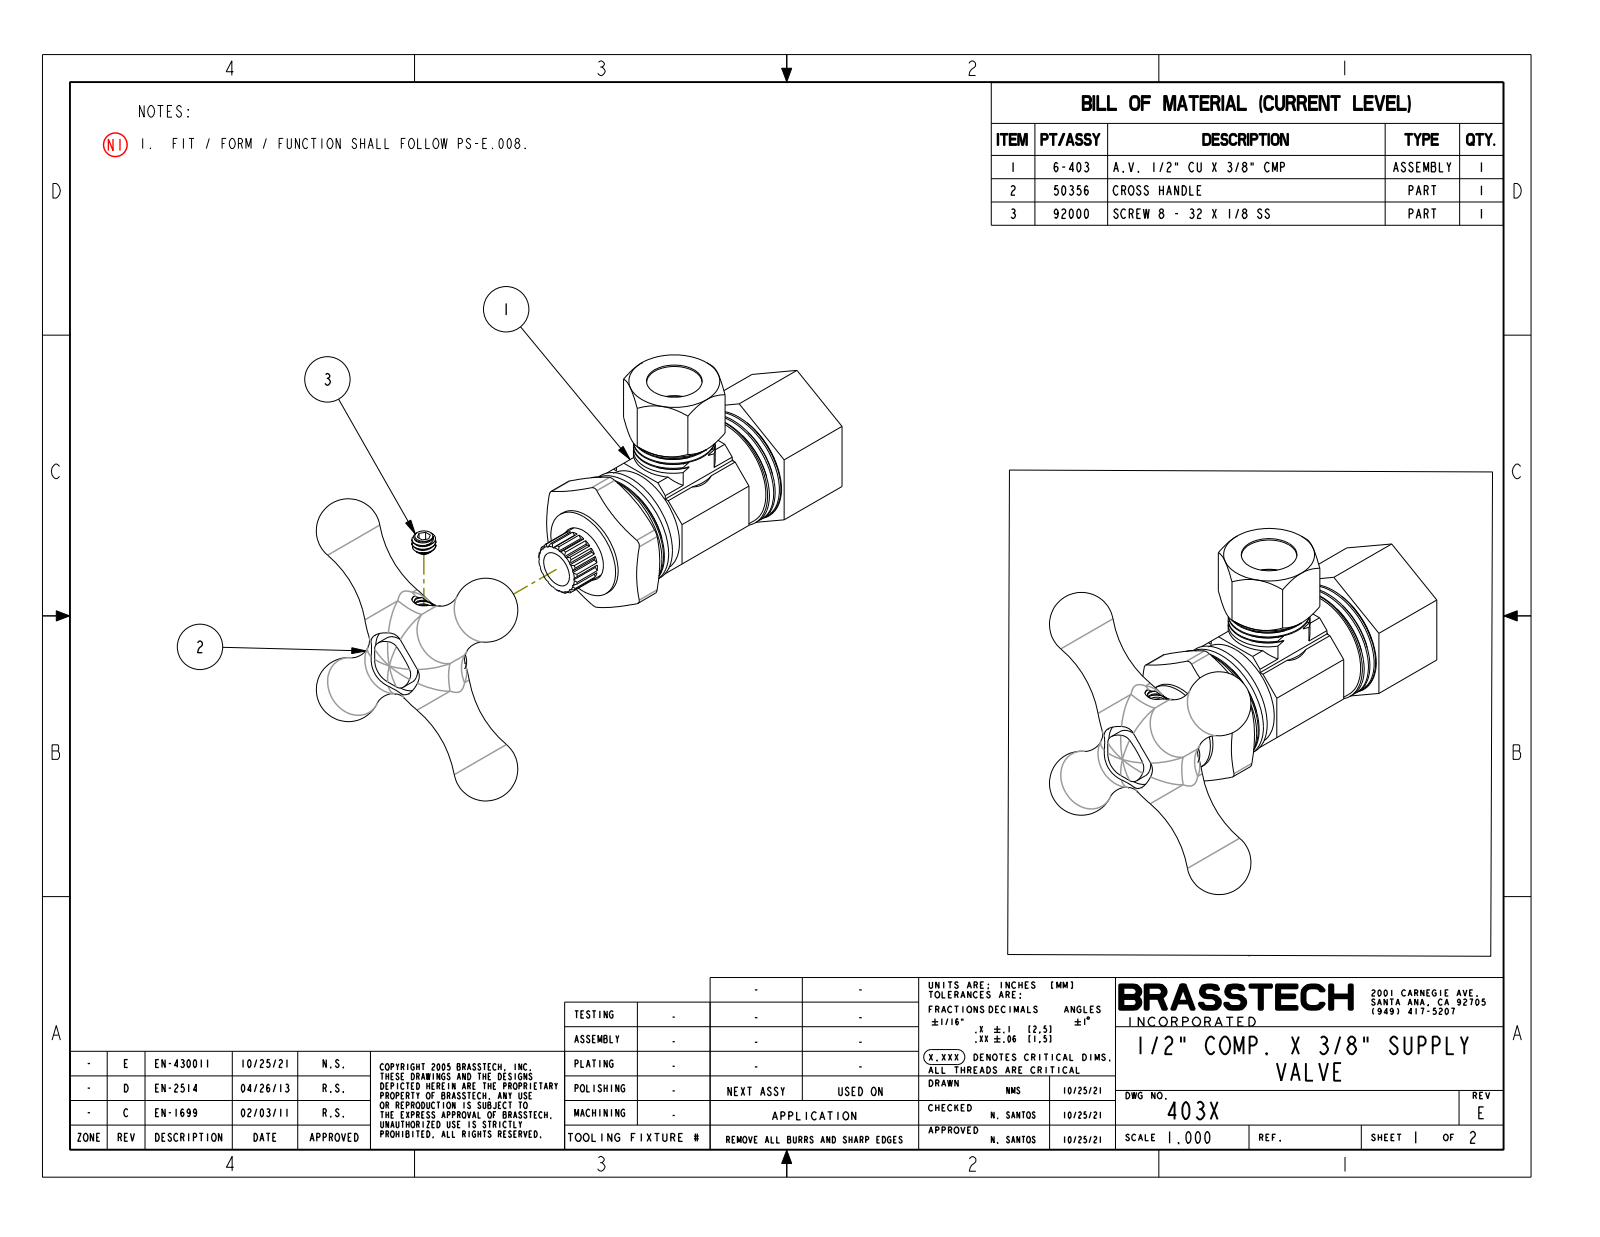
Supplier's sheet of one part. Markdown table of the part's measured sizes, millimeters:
| quantity | value |
| --- | --- |
| part name | 403X |
| STEP written by | CREO PARAMETRIC BY PTC INC, 2018500 (CONFIG_CONTROL_DESIGN) |
| units | millimeters |
| bodies | 3 solids, 772 faces (255 planar, 215 cylindrical, 302 other) |
| overall size | 66.5 × 48.2 × 45.1 |
| volume | 19 010 mm³ |
| surface area | 25 410 mm² |
| round holes (diameter × count) | 3.3 × 1, 9.5 × 1, 9.7 × 1, 9.7 × 1, 10 × 1, 10.2 × 1, 11.8 × 1, 12.2 × 1, 13.1 × 1, 14.3 × 1, 15.9 × 1, 19.1 × 1 |
| round bosses / shafts (diameter × count) | 21.8 × 1, 19.1 × 1, 18.2 × 1, 17.3 × 1, 17.2 × 1, 16 × 1, 13.7 × 1, 11.7 × 1 |
| partial cylindrical surfaces (radius × count) | 0.3 × 18, 1.3 × 6, 2.1 × 1, 4.4 × 1, 9.6 × 1 |
| main face-to-face distances | 22.2, 15.9, 3.2, 19.1, 20.3, 0.9, 21.3, 2.2, 18.1, 23.2 |
| hole center spacings | 27.7 |
